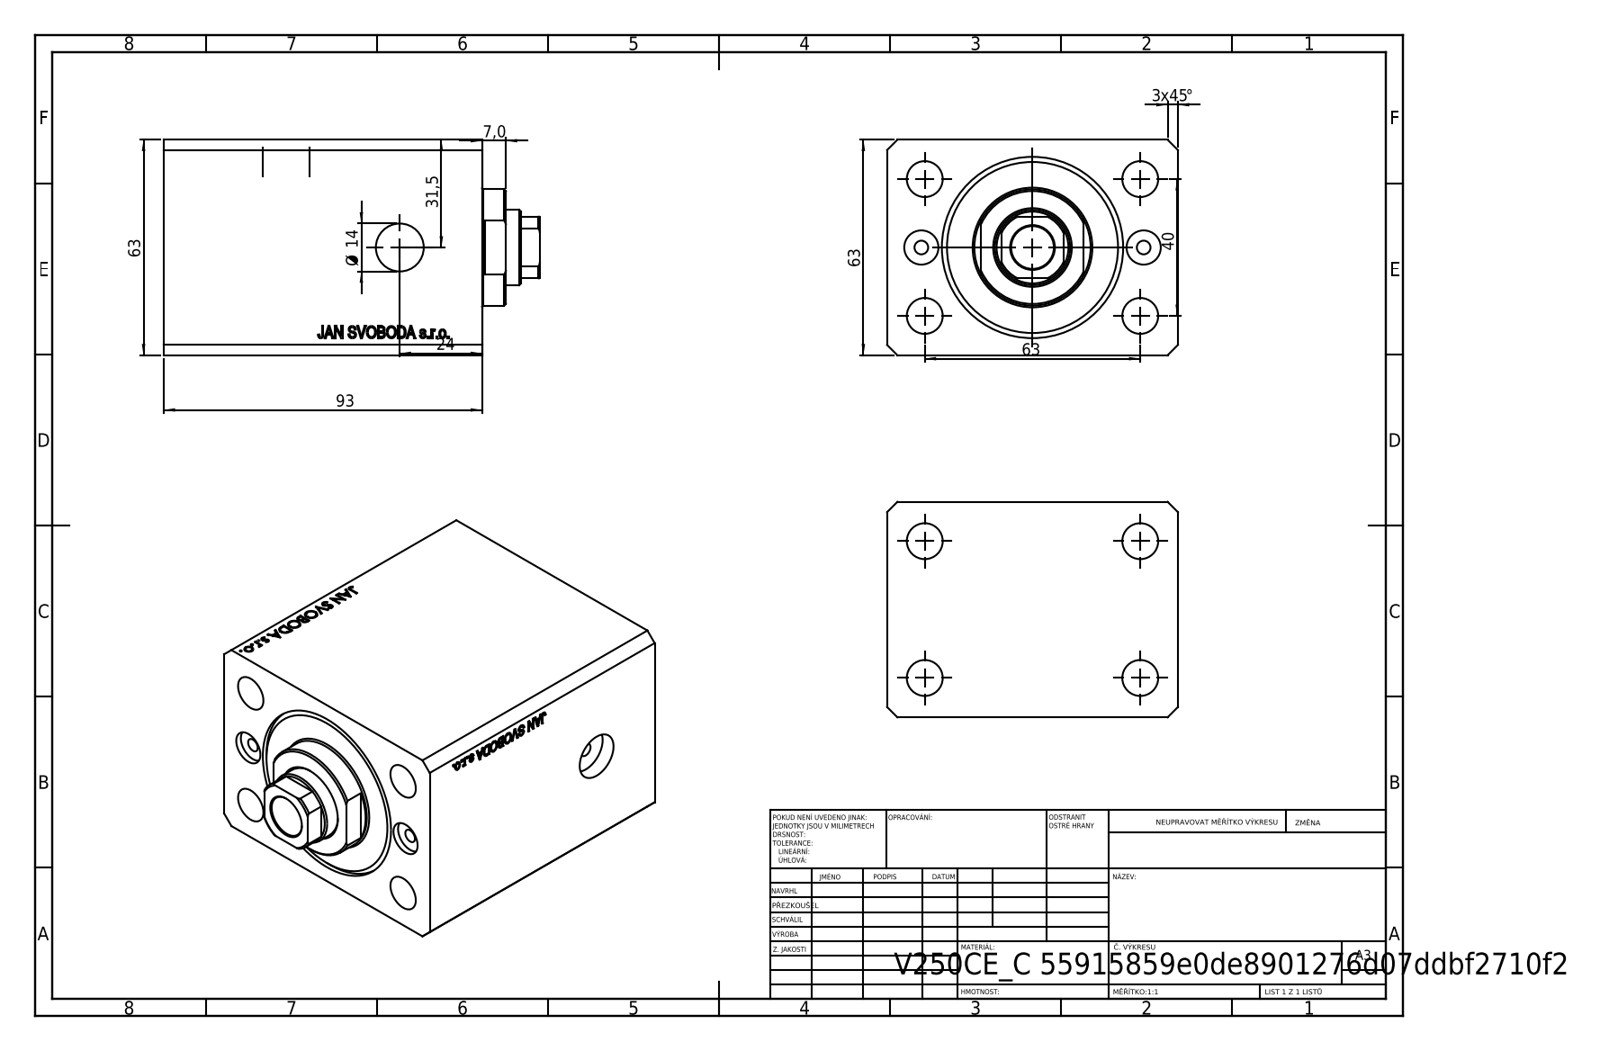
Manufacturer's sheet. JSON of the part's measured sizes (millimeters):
{"part_name": "V250CE_C_VCP; V250CE_C_Body; V250CE_VC_C", "step_written_by": "SolidWorks 2019 (CONFIG_CONTROL_DESIGN)", "units": "millimeters", "bodies": {"solids": 3, "faces": 862, "planar": 428, "cylindrical": 42, "other": 392}, "overall_size": [109.9, 85, 63], "volume_mm3": 450121, "surface_area_mm2": 85788, "round_holes": [[10.5, 4], [4, 3], [10, 2], [14, 2], [12.5, 1], [22, 1], [40, 1], [53, 1]], "round_bosses_or_shafts": [[34, 1]], "partial_cylinders_radius": [[10.5, 1]], "face_to_face_distances": [63, 85, 93, 65.9, 27.1, 11.4, 54.5, 81.6, 45.9, 34.5], "hole_center_spacings": [20.02, 37.31, 67.05, 32.5, 40, 63, 74.63, 45]}
